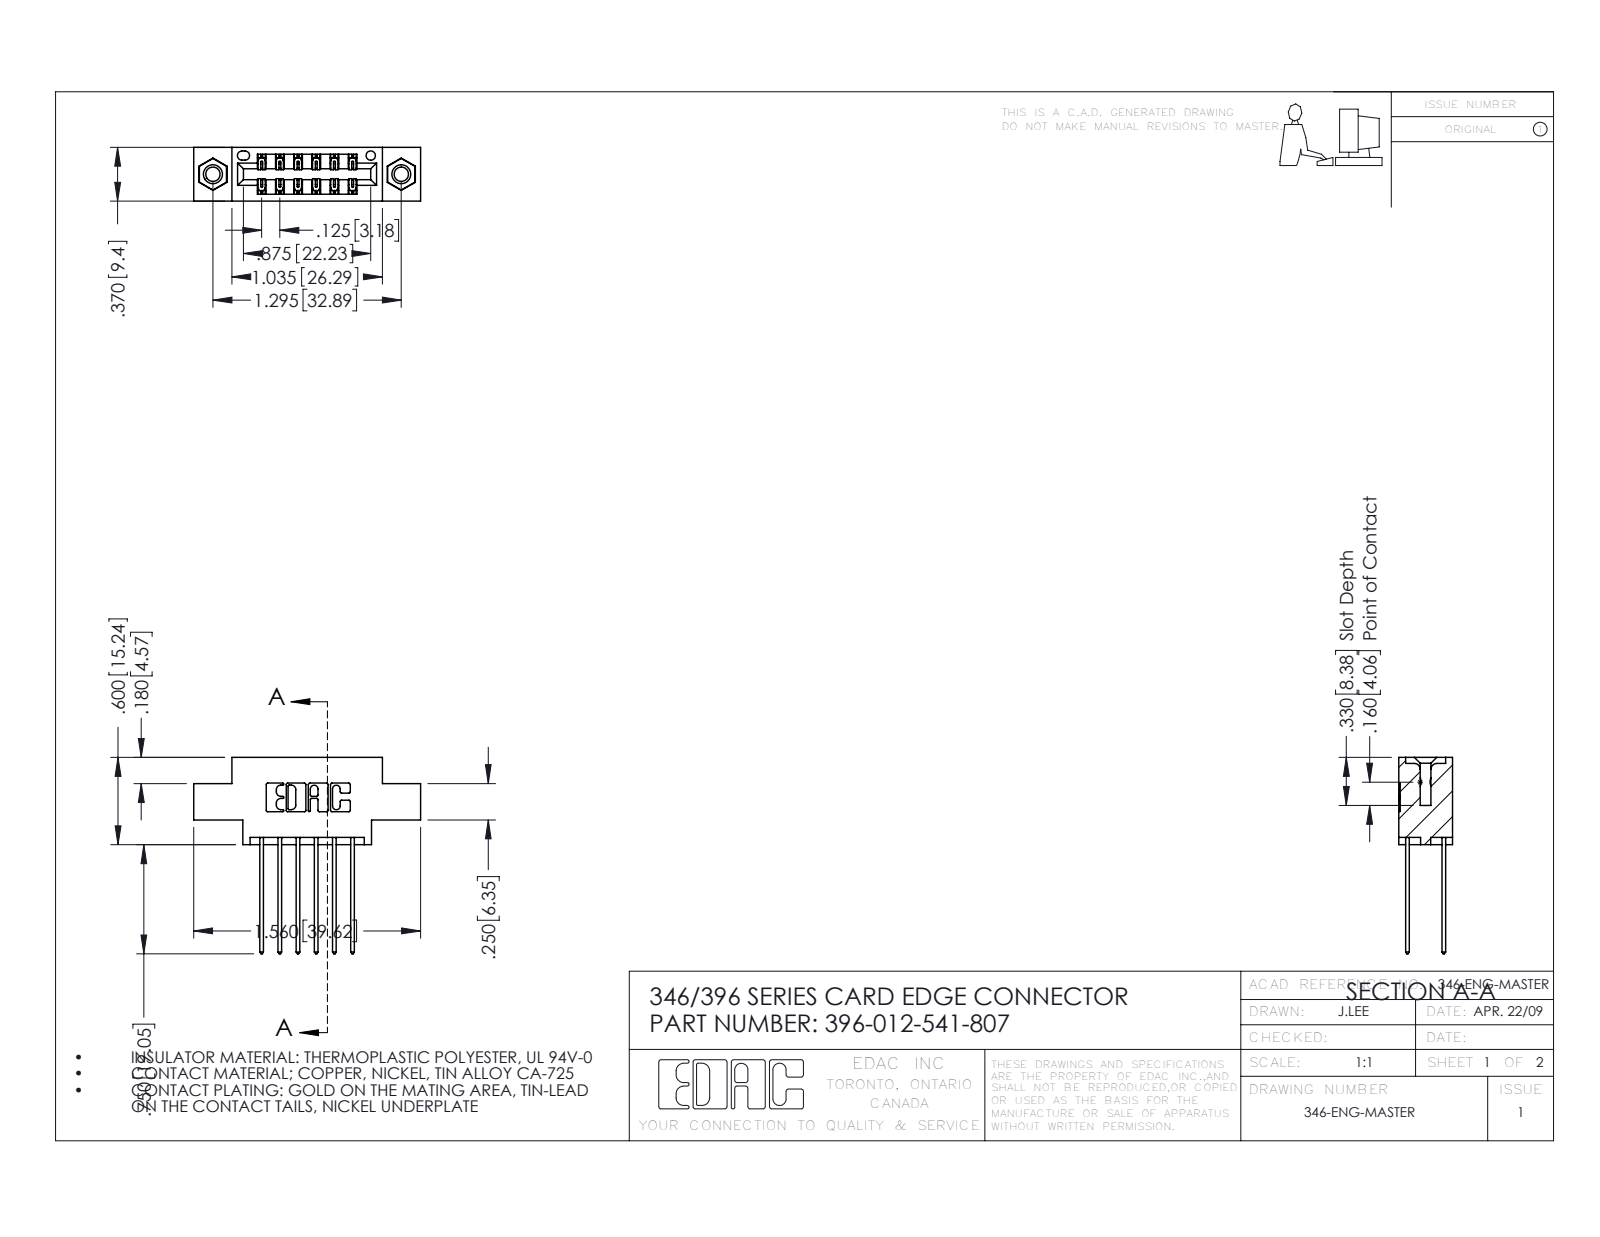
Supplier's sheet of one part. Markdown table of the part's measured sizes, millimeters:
| quantity | value |
| --- | --- |
| part name | 345-292-001_345-293-141; 345-250-001_345-250-005-103; 396-012-541-807; 346 Part_0.170 Offset - 0.156 Dia-TI |
| STEP written by | SolidWorks 2016 (CONFIG_CONTROL_DESIGN) |
| units | millimeters |
| bodies | 15 solids, 810 faces (532 planar, 262 cylindrical, 16 other) |
| overall size | 39.6 × 34.3 × 9.4 |
| volume | 3 490 mm³ |
| surface area | 4 768 mm² |
| round holes (diameter × count) | 2.5 × 2, 3.2 × 2, 4 × 2, 1.6 × 1 |
| round bosses / shafts (diameter × count) | 3.9 × 2 |
| partial cylindrical surfaces (radius × count) | 0.3 × 22, 0.2 × 18, 0.3 × 12, 0.2 × 6, 0.8 × 6, 0.7 × 3, 0.4 × 2, 0.6 × 2 |
| main face-to-face distances | 6.4, 1.2, 8.2, 9.4, 1.8, 7.6, 0.6, 7, 5.6, 3.8 |
| hole center spacings | 6.2, 27.7, 32.9 |
